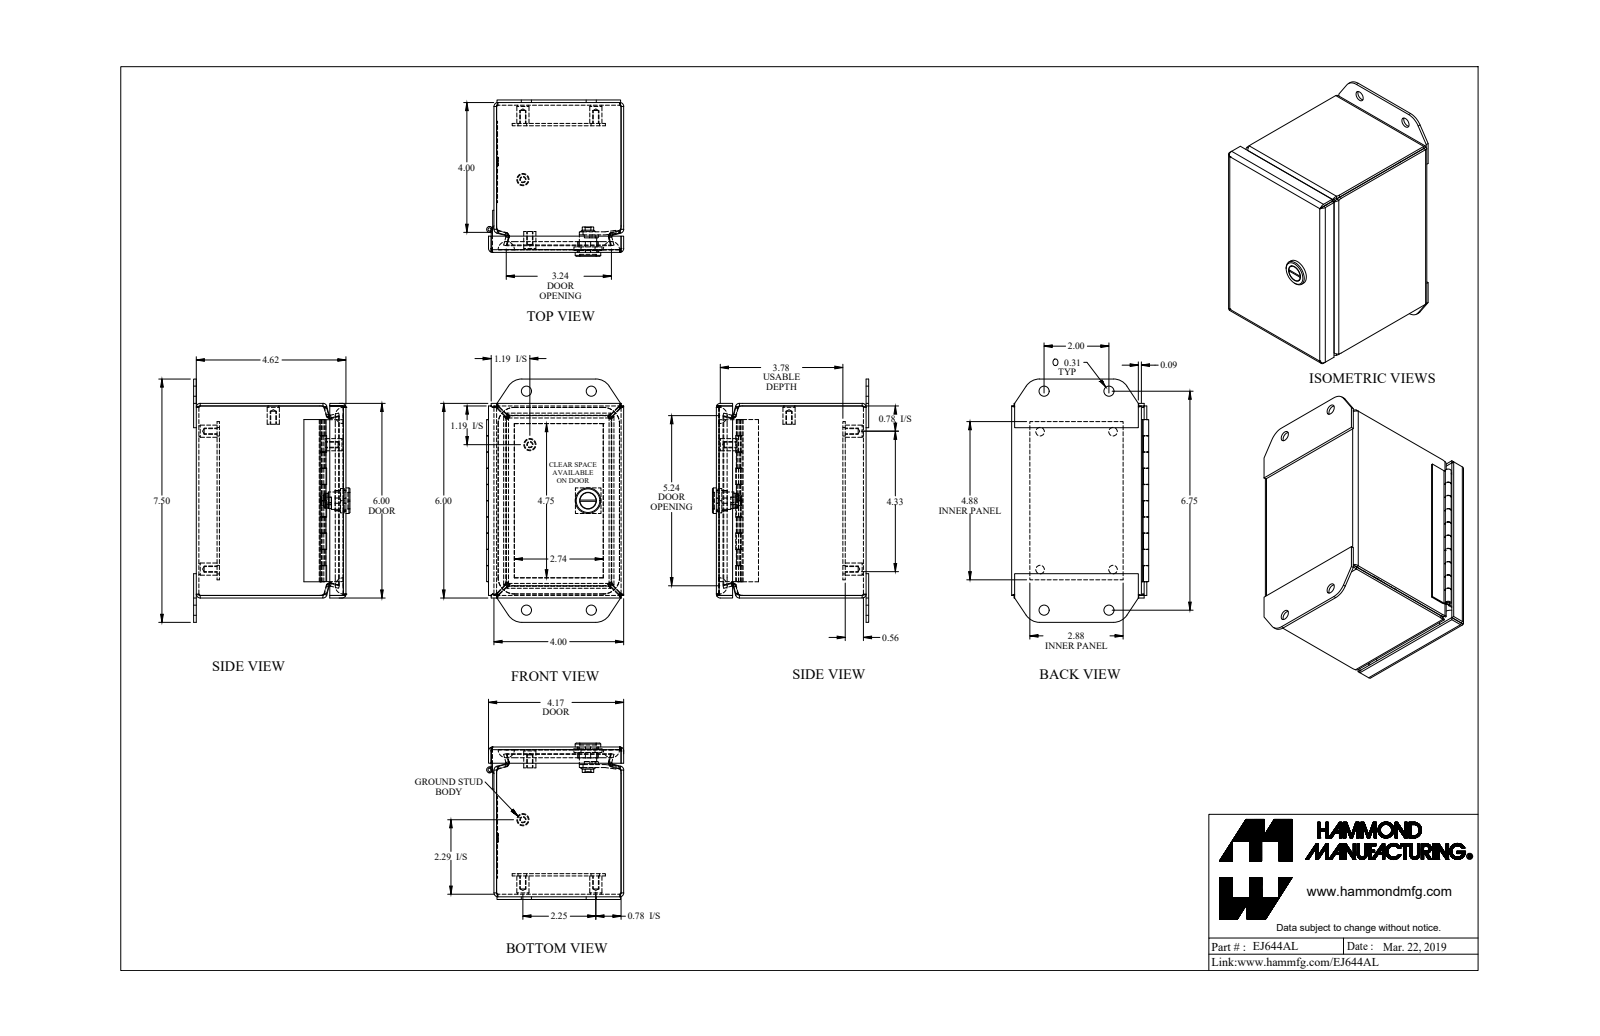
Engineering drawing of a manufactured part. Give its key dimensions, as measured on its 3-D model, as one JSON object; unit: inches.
{"part_name": "EJ644AL_Default", "step_written_by": "SolidWorks 2019 (CONFIG_CONTROL_DESIGN)", "units": "inches", "bodies": {"solids": 14, "faces": 550, "planar": 330, "cylindrical": 152, "other": 68}, "overall_size": [7.5, 4.82, 4.226], "volume_in3": 15.91, "surface_area_in2": 407, "round_holes": [[0.159, 6], [0.265, 4], [0.313, 4], [0.516, 1]], "round_bosses_or_shafts": [[0.375, 6], [0.33, 6], [0.788, 1], [0.535, 1], [0.496, 1], [0.435, 1], [0.18, 1], [0.1, 1]], "partial_cylinders_radius": [[0.041, 16], [0.121, 16], [0.281, 12], [0.25, 4], [0.499, 4], [0.5, 4], [0.06, 2], [0.03, 1]], "face_to_face_distances": [0.081, 4.536, 3.919, 4.617, 5.919, 4, 3.838, 4.455, 5.838, 6], "hole_center_spacings": [0.024, 1.256, 2.25, 4.809, 5.501, 2, 2.137, 2.233]}
